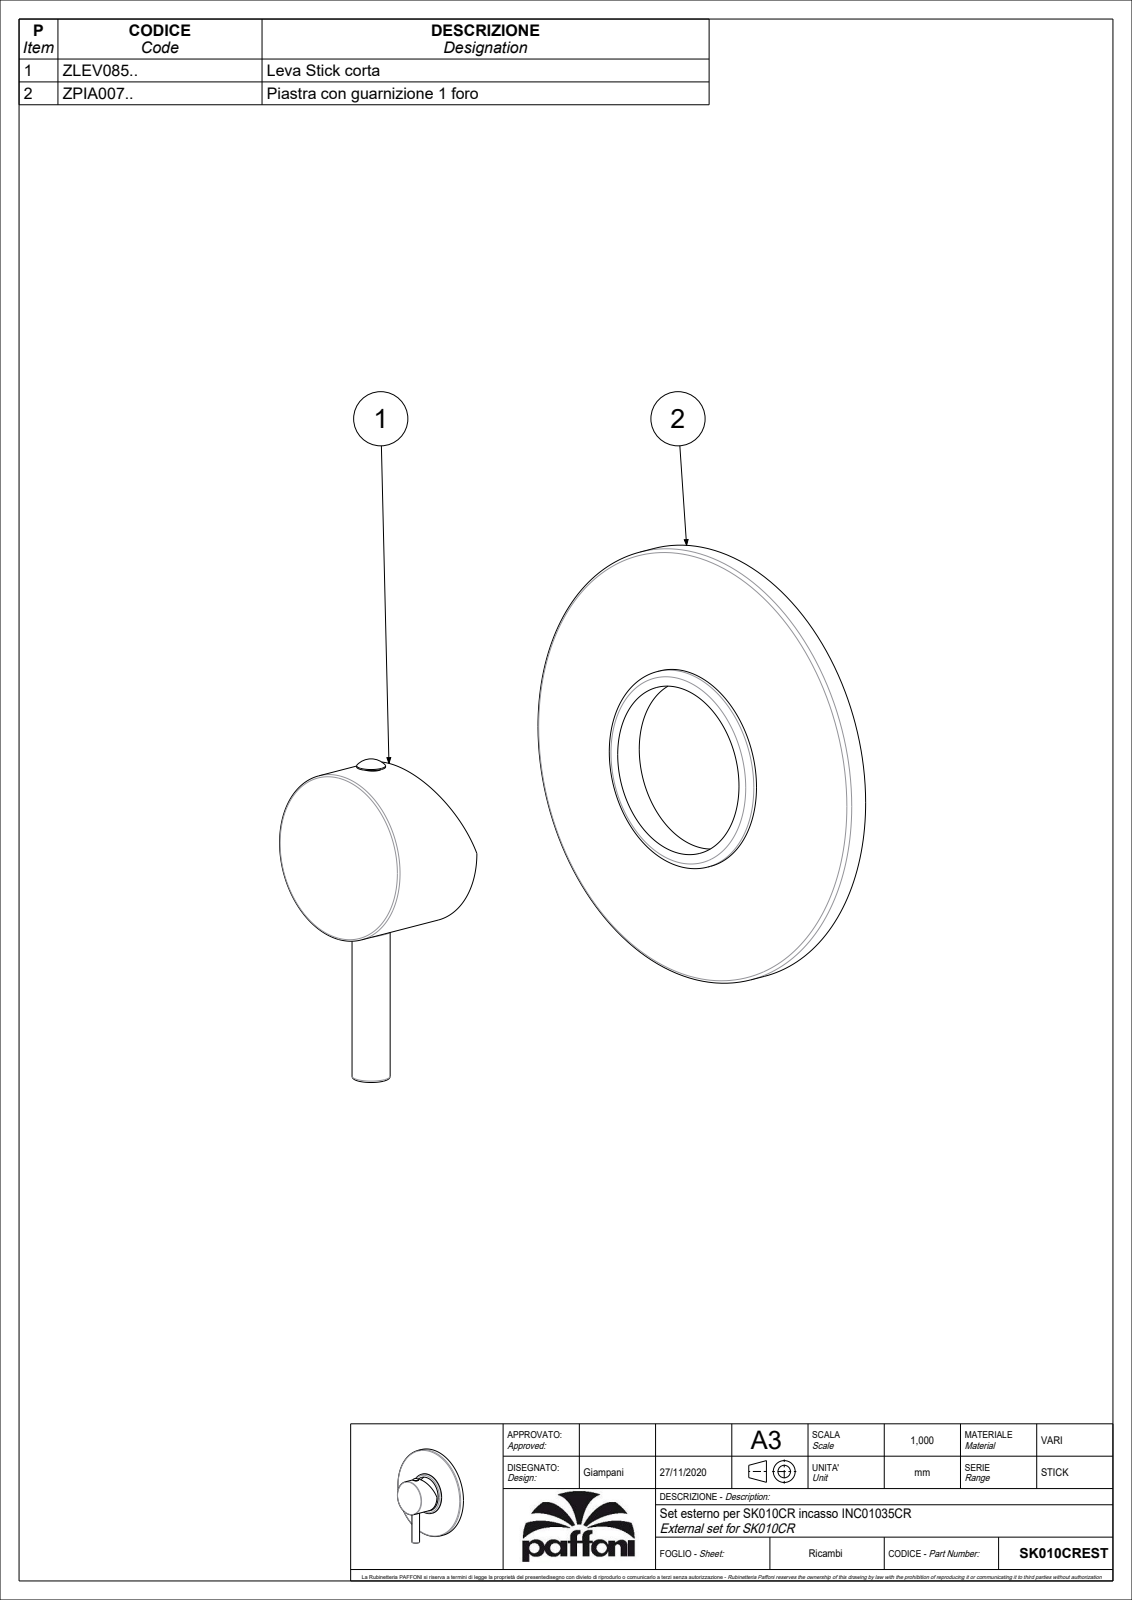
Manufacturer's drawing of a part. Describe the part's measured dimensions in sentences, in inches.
The part is named "SK010CREST". Its 3-D file was written by "CREO PARAMETRIC BY PTC INC, 2020044 (CONFIG_CONTROL_DESIGN)". It is 2 solids with 191 faces: 48 planar, 54 cylindrical and 89 other. Overall it measures 4.724 by 4.567 by 1.689 inches. Its volume is 1.672 cubic inches and its surface area 57.6 square inches. Round holes: 1 of diameter 0.118, 1 of diameter 1.772, 1 of diameter 1.969, 1 of diameter 4.488. Round bosses or shafts: 1 of diameter 4.567, 1 of diameter 2.087, 1 of diameter 1.752, 1 of diameter 0.394, 1 of diameter 0.299, 1 of diameter 0.217, 1 of diameter 0.197. Partial cylindrical surfaces (rounded edges, fillets, slot ends): 8 of radius 0.02. The main face-to-face distances are 0.157, 1.063, 0.453, 1.516, 0.098, 0.315, 0.354, 1.161, 0.059, 0.138.
